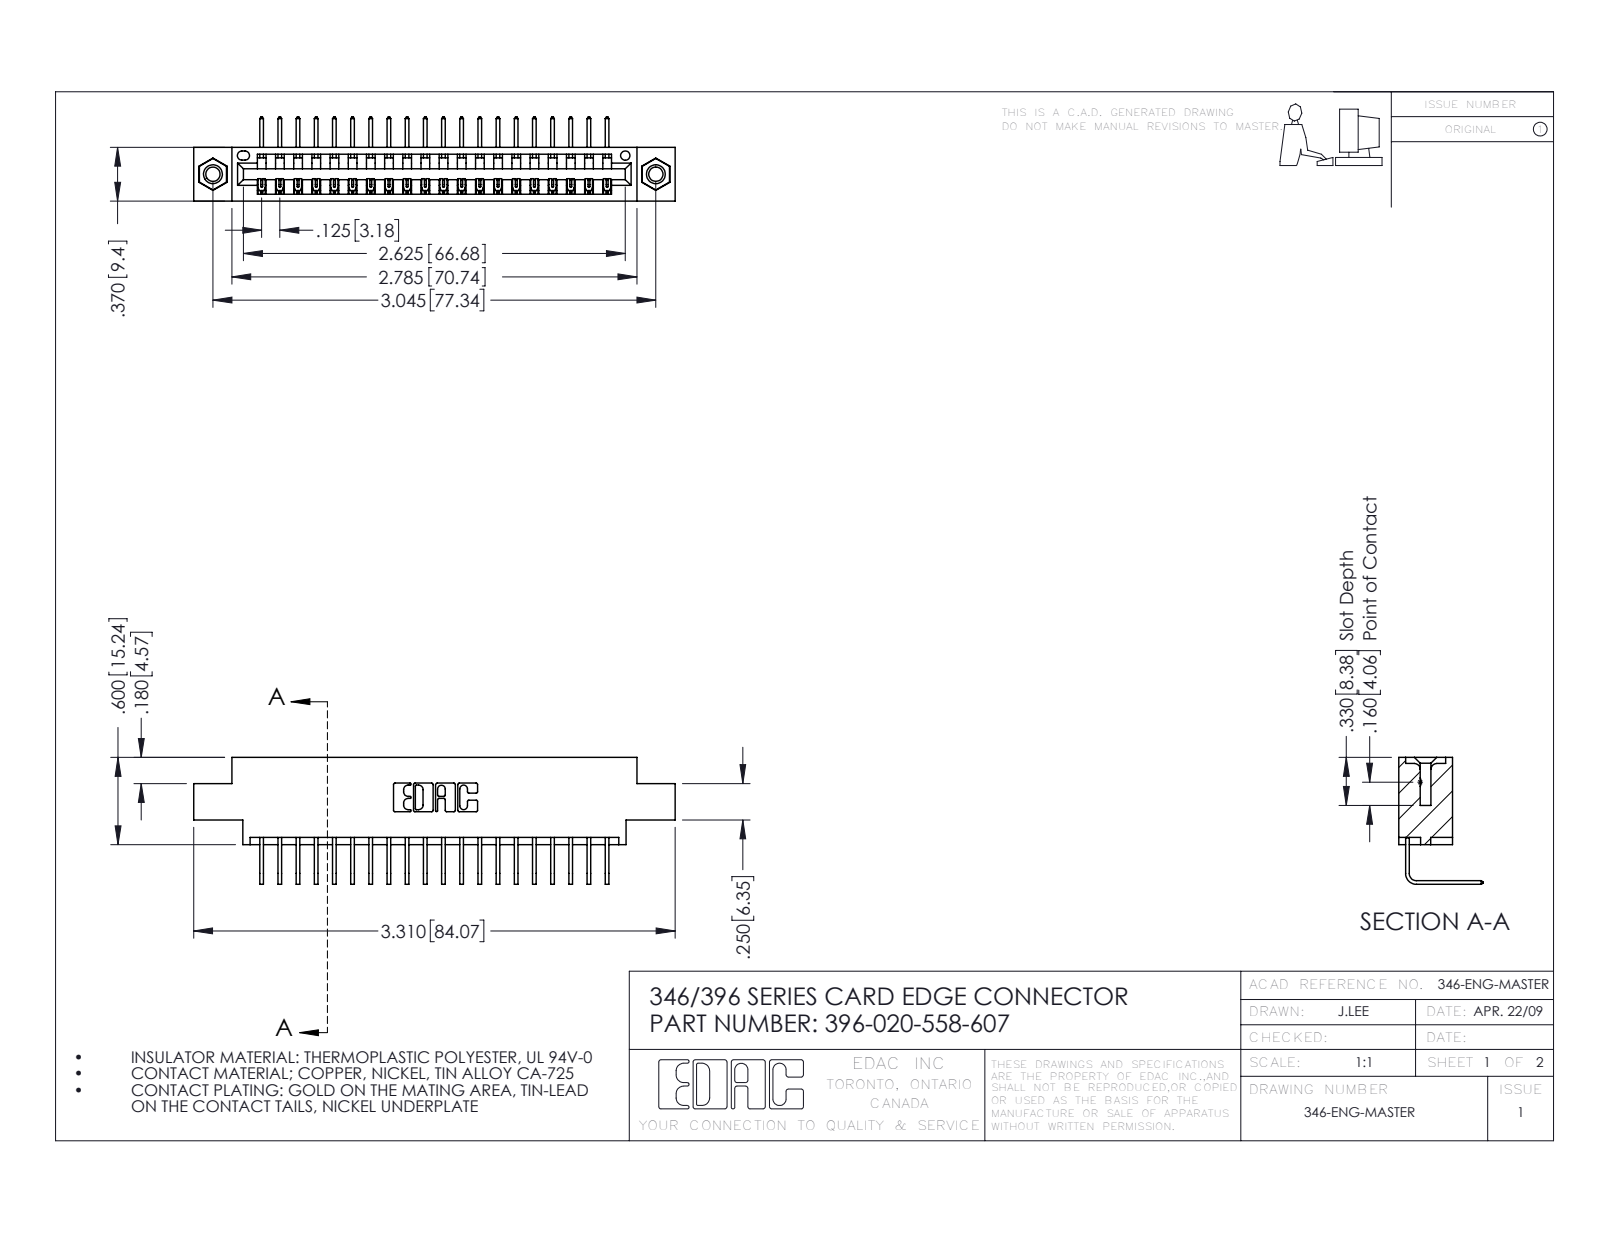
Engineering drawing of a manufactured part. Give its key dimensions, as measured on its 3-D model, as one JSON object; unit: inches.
{"part_name": "396-020-558-607; 345-292-001_558 Tail - 2; 346 Part_0.170 Offset - 0.156 Dia-TI; 345-250-001_345-250-005-103", "step_written_by": "SolidWorks 2016 (CONFIG_CONTROL_DESIGN)", "units": "inches", "bodies": {"solids": 23, "faces": 1386, "planar": 952, "cylindrical": 418, "other": 16}, "overall_size": [3.31, 0.873, 0.58], "volume_in3": 0.476, "surface_area_in2": 15.65, "round_holes": [[0.098, 2], [0.125, 2], [0.156, 2], [0.064, 1]], "round_bosses_or_shafts": [[0.155, 2]], "partial_cylinders_radius": [[0.006, 40], [0.01, 22], [0.007, 6], [0.031, 6], [0.026, 3], [0.031, 2], [0.04, 2], [0.014, 1]], "face_to_face_distances": [0.322, 0.048, 0.37, 0.25, 0.298, 0.025, 0.072, 0.222, 0.148, 0.1], "hole_center_spacings": [0.246, 2.837, 3.045]}
